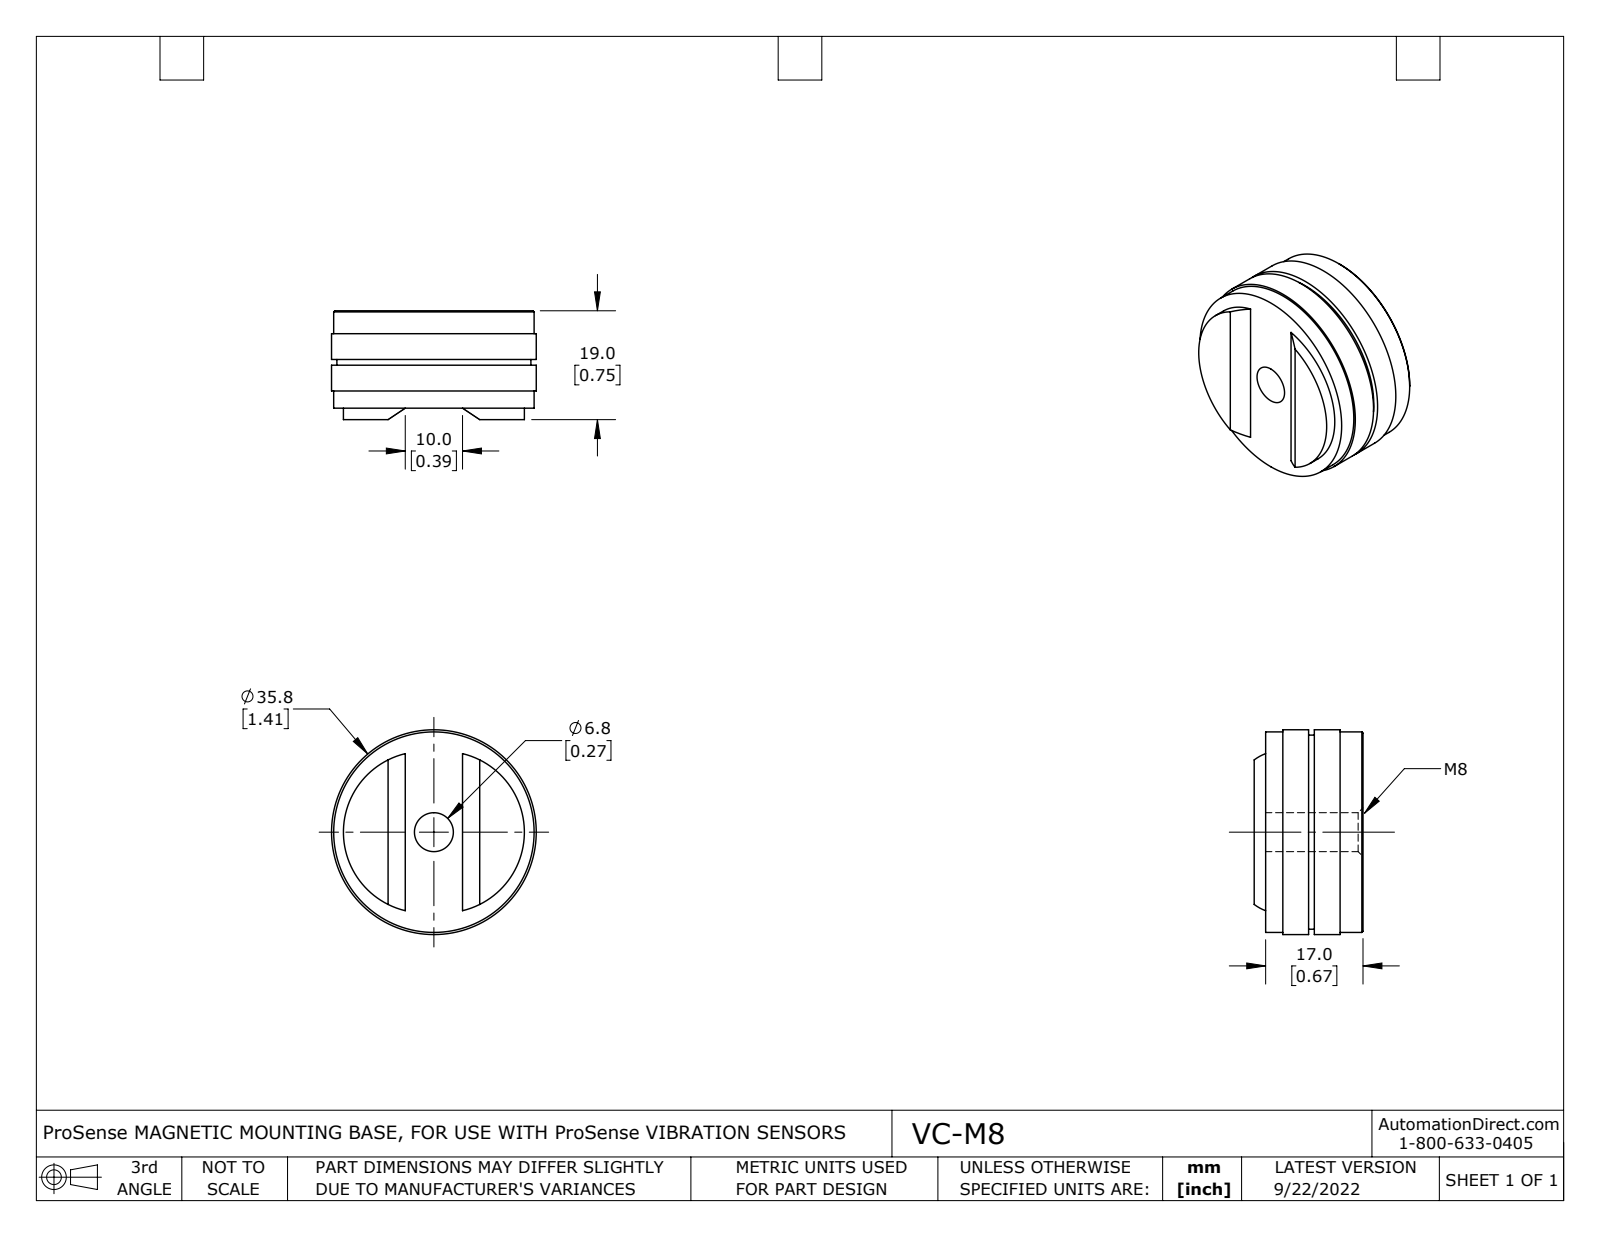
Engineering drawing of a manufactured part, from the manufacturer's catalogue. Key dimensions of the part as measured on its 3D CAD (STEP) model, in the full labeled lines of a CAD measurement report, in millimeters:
Part name (STEP PRODUCT): VC-MB
STEP written by: SolidWorks 2021 (AUTOMOTIVE_DESIGN)
Units: millimetres
Bodies: 1 solid, 28 faces (10 planar, 14 cylindrical, 4 other)
Overall size (bounding box): 35.7 × 35.7 × 19
Volume: 16 760 mm³ · Surface area: 4 537 mm²
Round holes (diameter × count): ⌀6.8 ×1
Round bosses / shafts (diameter × count): ⌀35.7 ×1, ⌀35 ×1, ⌀33.9 ×1
Partial cylindrical surfaces — rounded edges, fillets, slot ends (radius × count): R14.1 ×2
Main face-to-face distances: 17, 19, 2, 8.5, 9.5, 1, 10.5, 7.5, 4.5, 5.5
